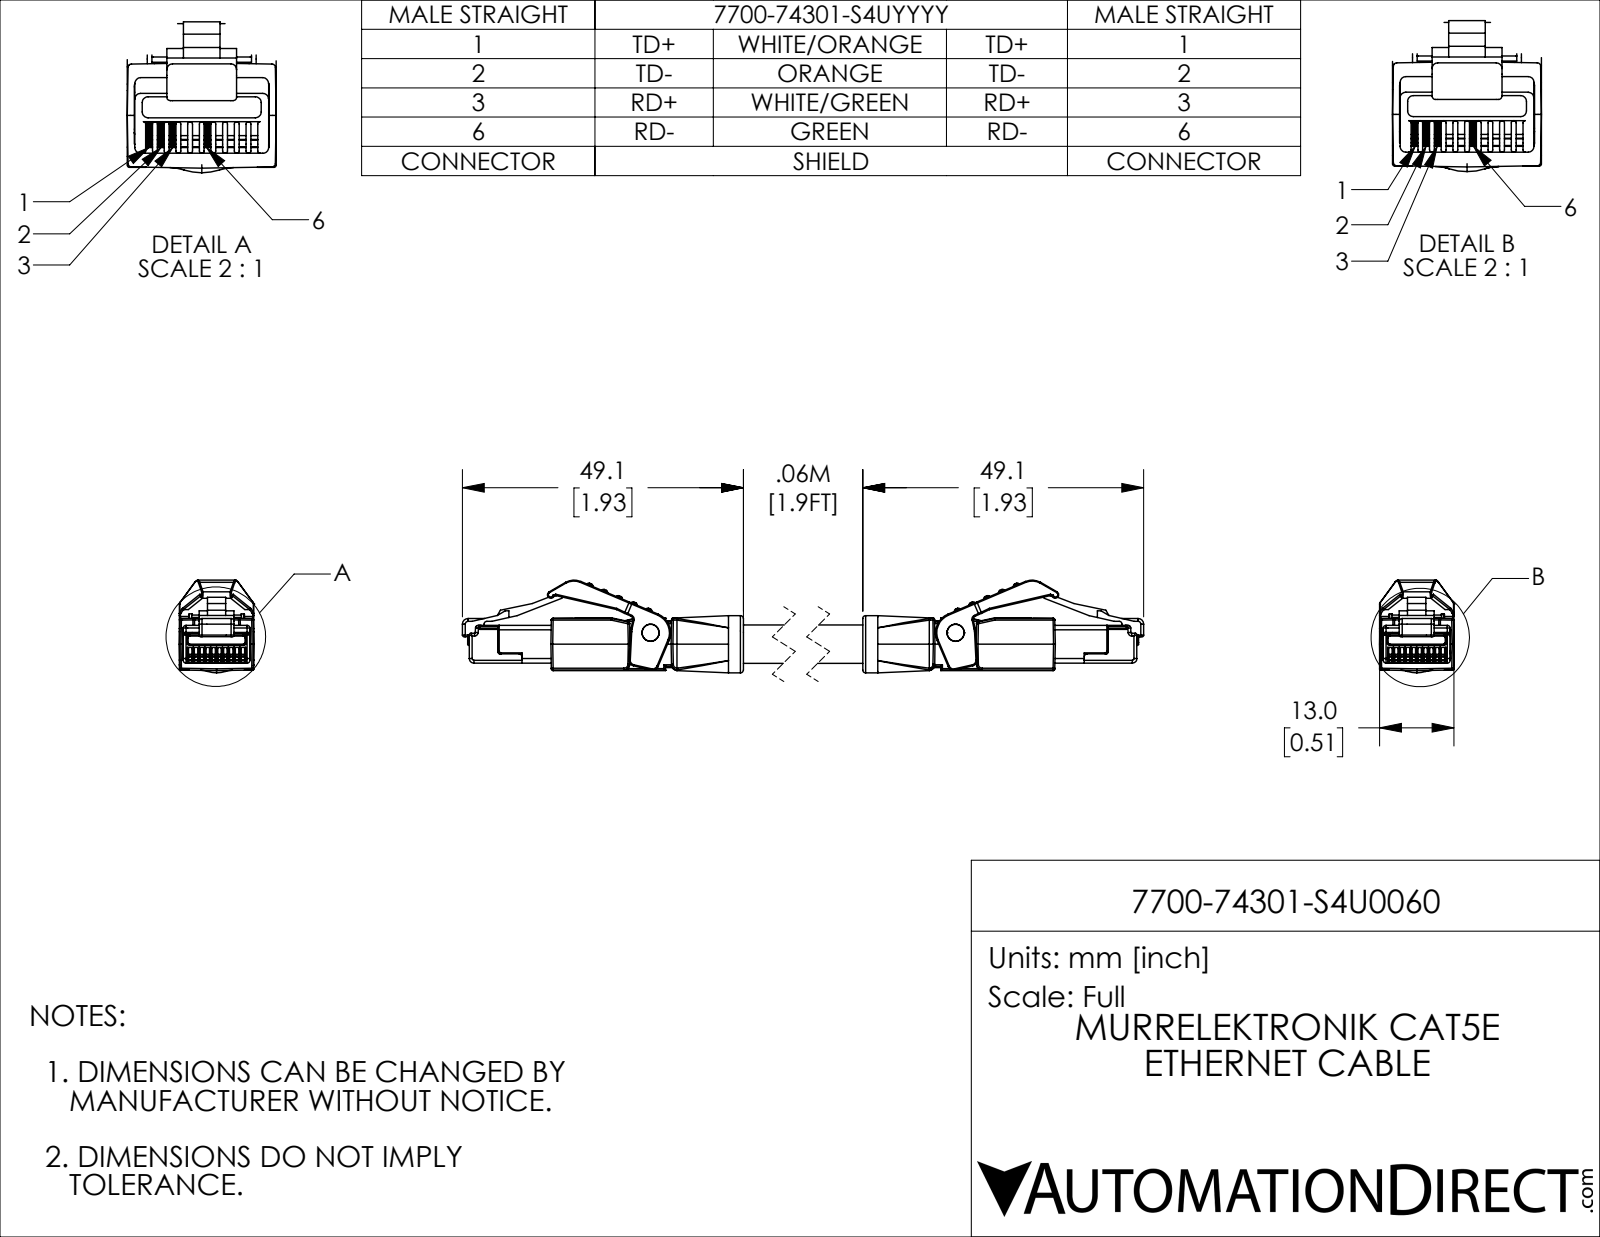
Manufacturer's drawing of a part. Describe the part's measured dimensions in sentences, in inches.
The part is named "7700-74301-S4U0060_1; 7700-74301-S4U0060". Its 3-D file was written by "SolidWorks 2021 (CONFIG_CONTROL_DESIGN)". It is 2 solids with 1406 faces: 568 planar, 566 cylindrical and 272 other. Overall it measures 5.112 by 0.638 by 0.512 inches. Its volume is 0.668 cubic inches and its surface area 10.82 square inches. Round holes: 2 of diameter 0.118. Round bosses or shafts: 2 of diameter 0.117, 1 of diameter 0.394, 1 of diameter 0.264. Partial cylindrical surfaces (rounded edges, fillets, slot ends): 136 of radius 0.008, 114 of radius 0.012, 40 of radius 0.004, 36 of radius 0.02, 10 of radius 0.039, 6 of radius 0.031, 4 of radius 0.079, 4 of radius 0.197. The main face-to-face distances are 0.512, 0.362, 0.024, 0.488, 0.026, 0.26, 0.069, 0.443, 0.045, 0.419. The hole center spacings are 2.526.
